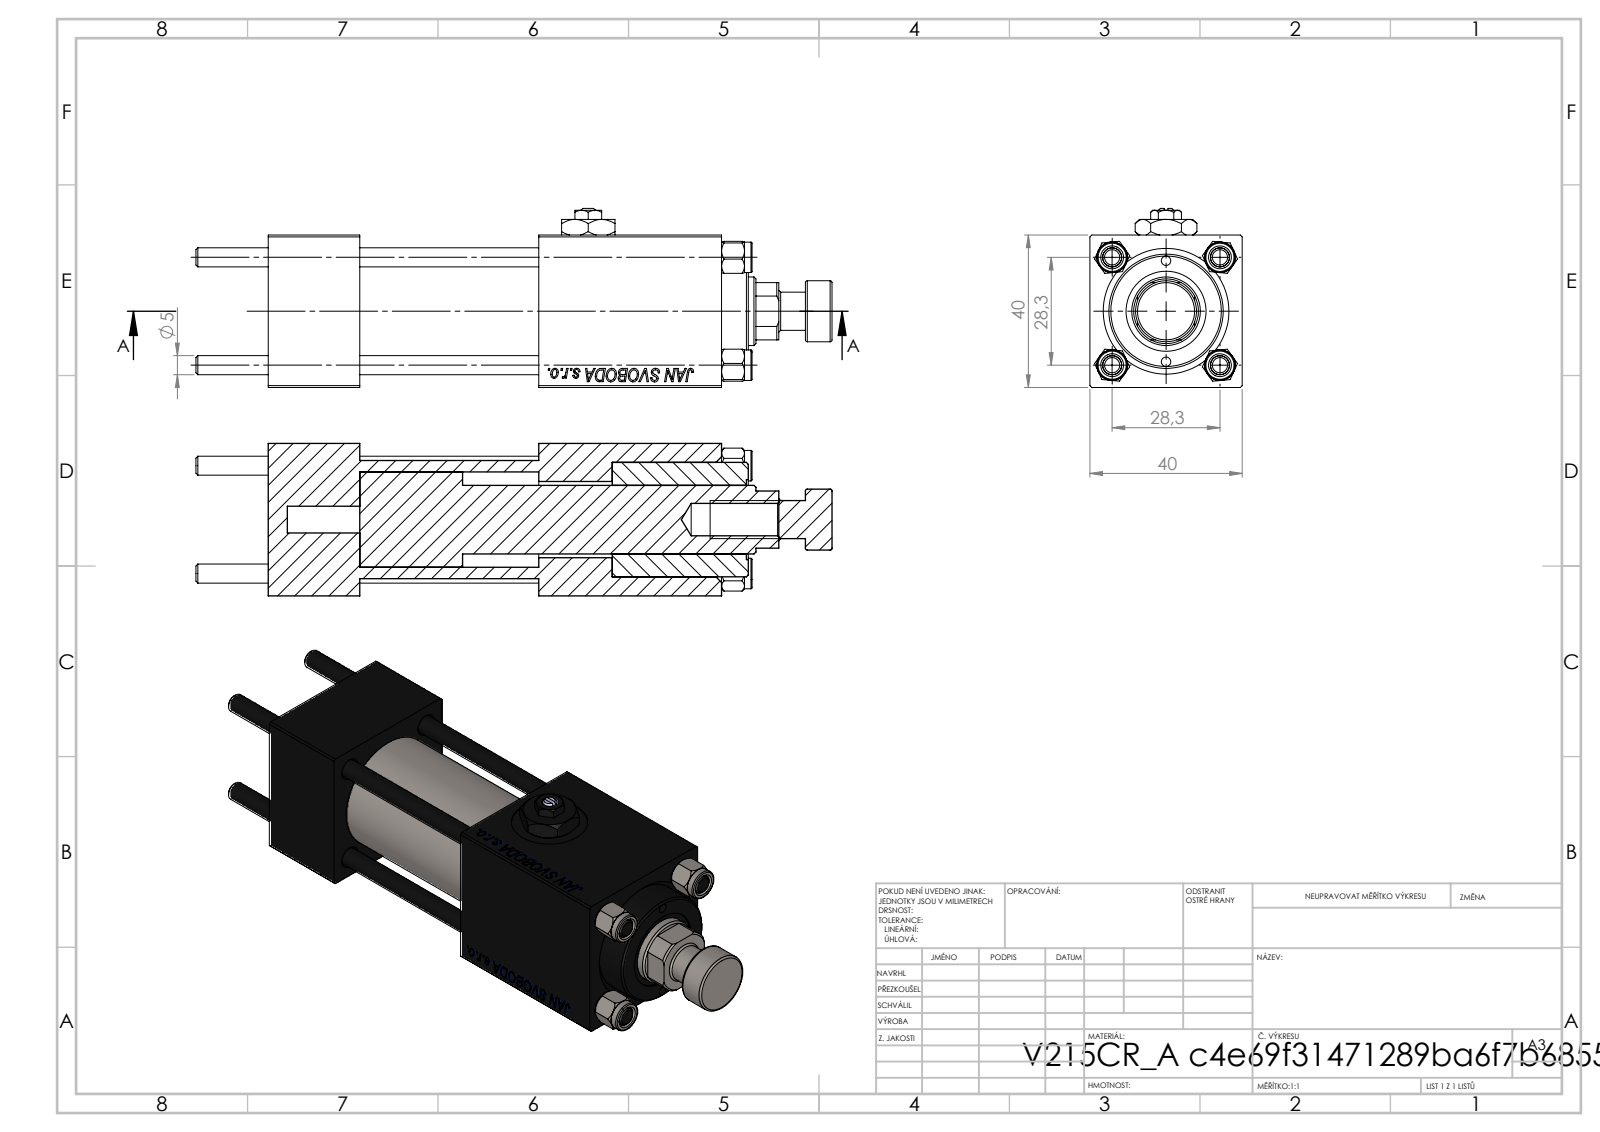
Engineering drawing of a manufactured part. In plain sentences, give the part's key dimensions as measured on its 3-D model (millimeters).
The part is named "V215CR_ROD_END_W; NUT_M5; CR025_012_A_0_G_A_G_M_020_+#_##_TYCINKA; V215_VC_A (+3 more)". Its 3-D file was written by "SolidWorks 2019 (CONFIG_CONTROL_DESIGN)". It is 13 solids with 1195 faces: 545 planar, 88 cylindrical and 562 other. Overall it measures 167 by 47 by 40 millimeters. Its volume is 153 618 cubic millimeters and its surface area 63 055 square millimeters. Round holes: 4 of diameter 5, 3 of diameter 20, 2 of diameter 2.5, 2 of diameter 7, 2 of diameter 13.16, 1 of diameter 8.5, 1 of diameter 18, 1 of diameter 21, 1 of diameter 25, 1 of diameter 30. Round bosses or shafts: 4 of diameter 8, 1 of diameter 31, 1 of diameter 16, 1 of diameter 10. Partial cylindrical surfaces (rounded edges, fillets, slot ends): 1 of radius 8.5. The main face-to-face distances are 40, 24, 71, 47, 90.3, 66.3, 19.3, 119, 95, 48. The hole center spacings are 14.18, 20.01, 28.3, 30.84, 13.25, 40.02, 26.5, 72.
